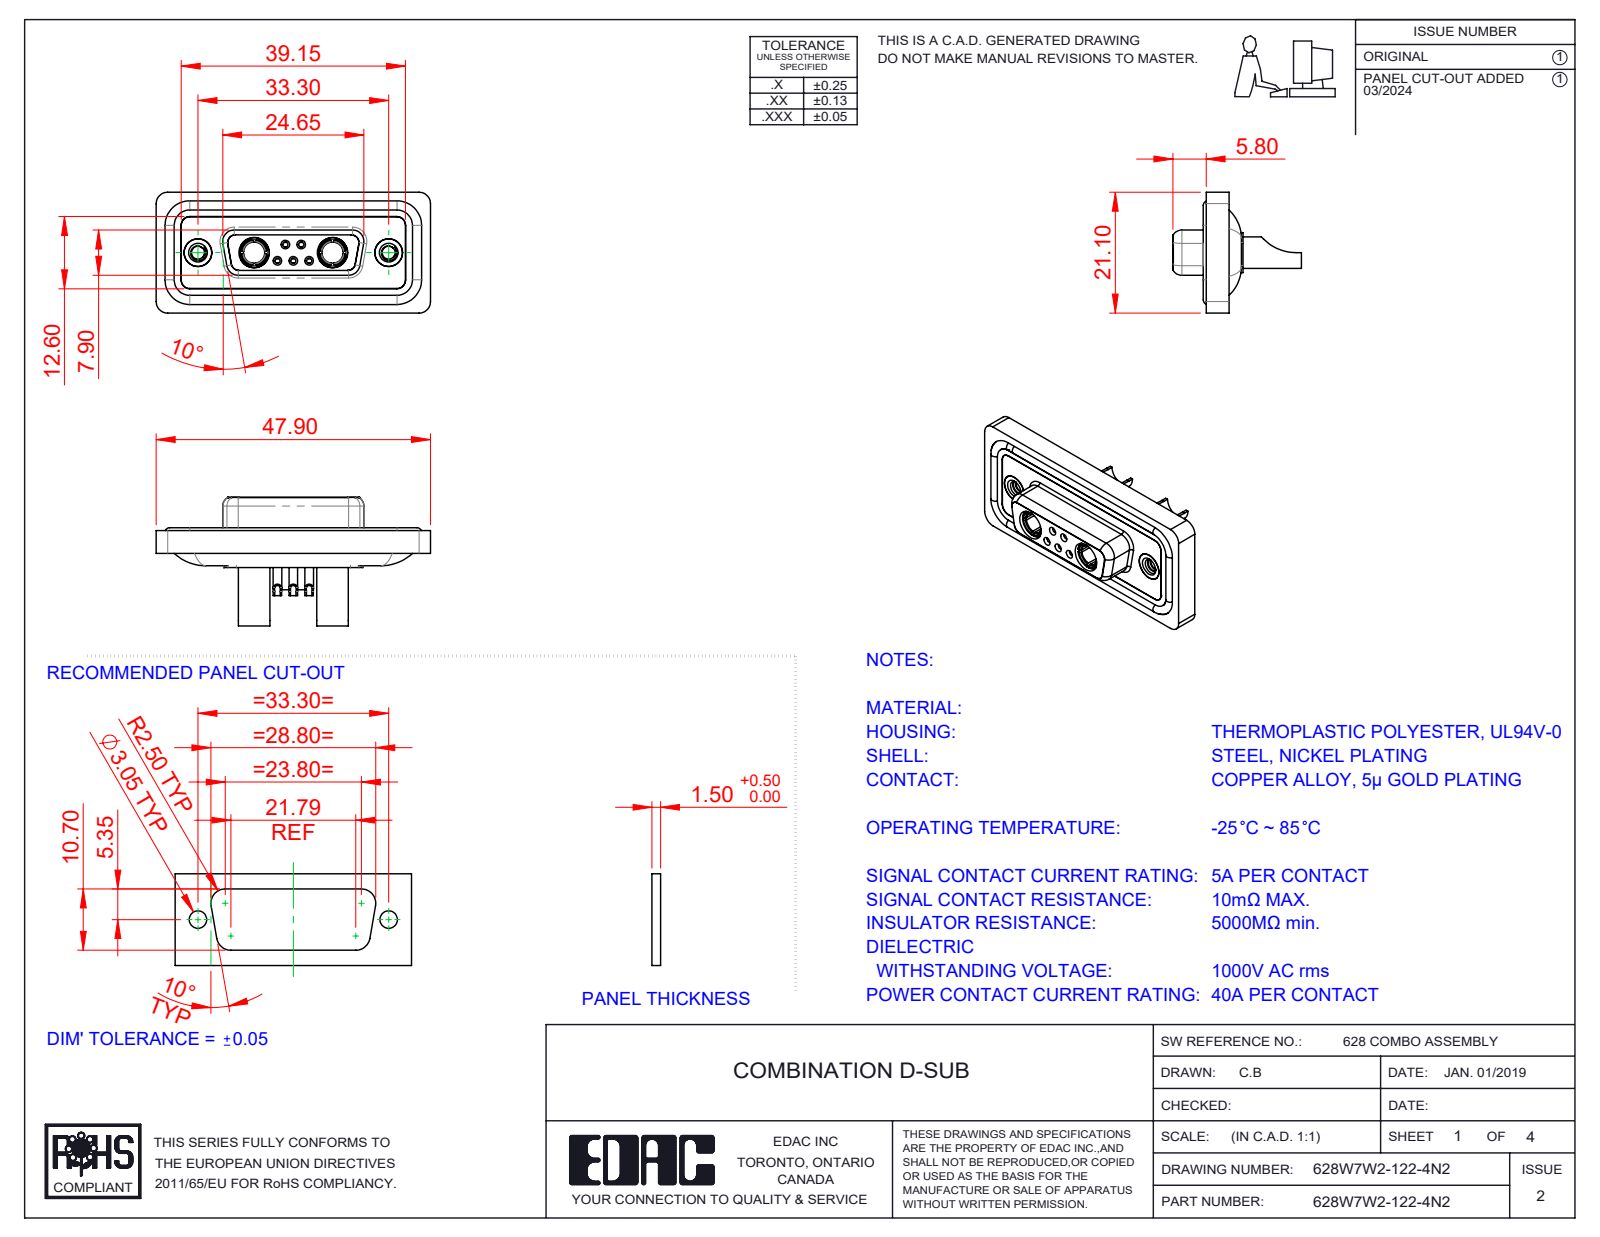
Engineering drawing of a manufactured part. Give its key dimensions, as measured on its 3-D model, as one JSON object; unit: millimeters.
{"part_name": "628Combo Contact Row 2_22; 628Combo Threaded Rivet_2; 628Combo Shell Front_15 Contacts; Power Socket_40A SC (+5 more)", "step_written_by": "SolidWorks 2023 (CONFIG_CONTROL_DESIGN)", "units": "millimeters", "bodies": {"solids": 16, "faces": 815, "planar": 252, "cylindrical": 341, "other": 222}, "overall_size": [47.9, 22.45, 21.1], "volume_mm3": 6168, "surface_area_mm2": 10220, "round_holes": [[0.9, 5], [1, 5], [1.1, 5], [1.5, 5], [2, 5], [4.85, 4], [1.6, 3], [1.7, 2], [2.26, 2], [3.7, 2], [4, 2], [4.05, 2]], "round_bosses_or_shafts": [[1.6, 6], [2.2, 5], [5.5, 2], [5.2, 2], [4.96, 2], [4.95, 2], [4.8, 2], [4.75, 2]], "partial_cylinders_radius": [[1.5, 22], [2, 20], [1.35, 12], [1.6, 8], [1, 6], [0.25, 4], [0.5, 4], [0.6, 4]], "face_to_face_distances": [0.4, 1.6, 1.8, 0.5, 2.9, 1.1, 7.45, 5.65, 6.6, 7.05], "hole_center_spacings": [3.16, 2.77, 9.8, 23.5, 4.31, 4.33, 5.03, 5.04]}
